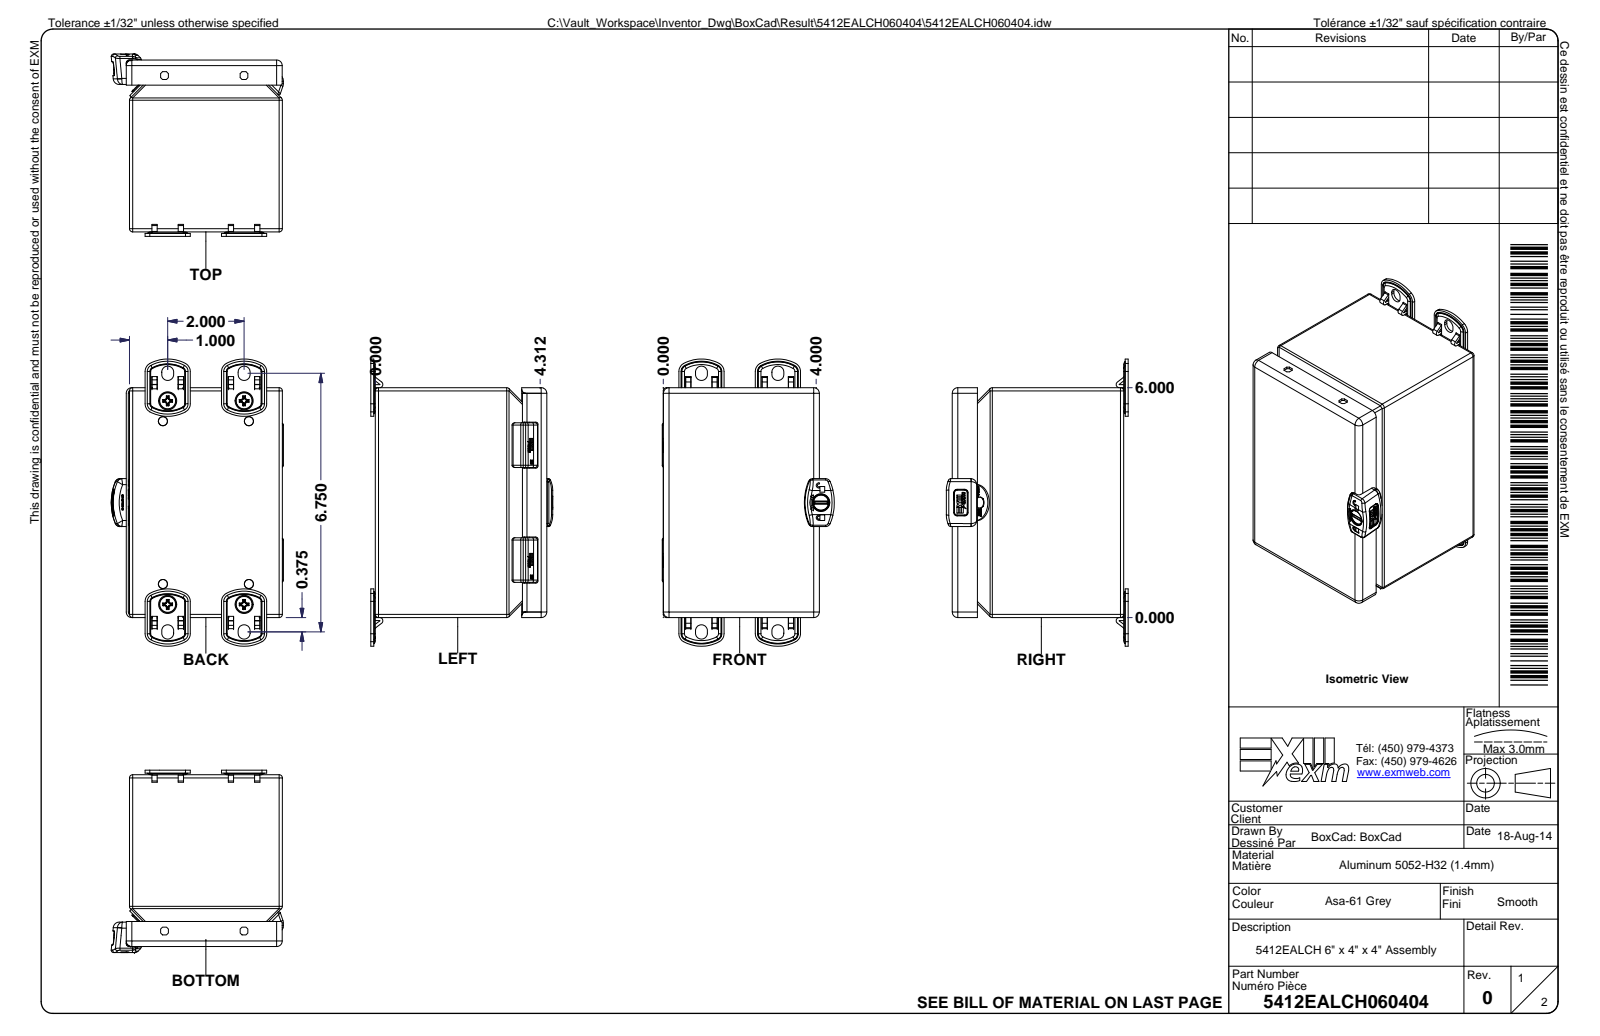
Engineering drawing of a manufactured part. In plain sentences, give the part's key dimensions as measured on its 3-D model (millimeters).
The part is named "5412EALCH060404; 5412EALCH060404B; 5412EALCH060404B-P; STK-S-00100 (+8 more)". Its 3-D file was written by "Autodesk Inventor 2024 (AUTOMOTIVE_DESIGN)". It is 48 solids with 5868 faces: 2726 planar, 1235 cylindrical and 1907 other. Overall it measures 190.4 by 120.8 by 112.8 millimeters. Its volume is 188 100 cubic millimeters and its surface area 264 600 square millimeters. Round holes: 6 of diameter 5, 4 of diameter 5, 4 of diameter 6, 4 of diameter 8.1, 3 of diameter 5.1, 2 of diameter 0.8, 2 of diameter 4.2, 2 of diameter 4.4, 2 of diameter 5.5, 2 of diameter 5.8, 2 of diameter 6, 2 of diameter 6.1. Round bosses or shafts: 8 of diameter 5.9, 4 of diameter 12.7, 4 of diameter 6, 3 of diameter 5, 2 of diameter 10, 2 of diameter 7.6, 2 of diameter 4.9, 2 of diameter 0.9. Partial cylindrical surfaces (rounded edges, fillets, slot ends): 157 of radius 0.2, 123 of radius 0.5, 73 of radius 1, 70 of radius 0.1, 51 of radius 0.3, 31 of radius 0.8, 27 of radius 2, 26 of radius 1.5. The main face-to-face distances are 1.3, 112.5, 100.3, 151.1, 111.1, 113.8, 101.6, 98.9, 1.3, 152.4. The hole center spacings are 13.9, 121.5, 122.1, 108, 55.6, 57.2, 55.7, 59.2.
